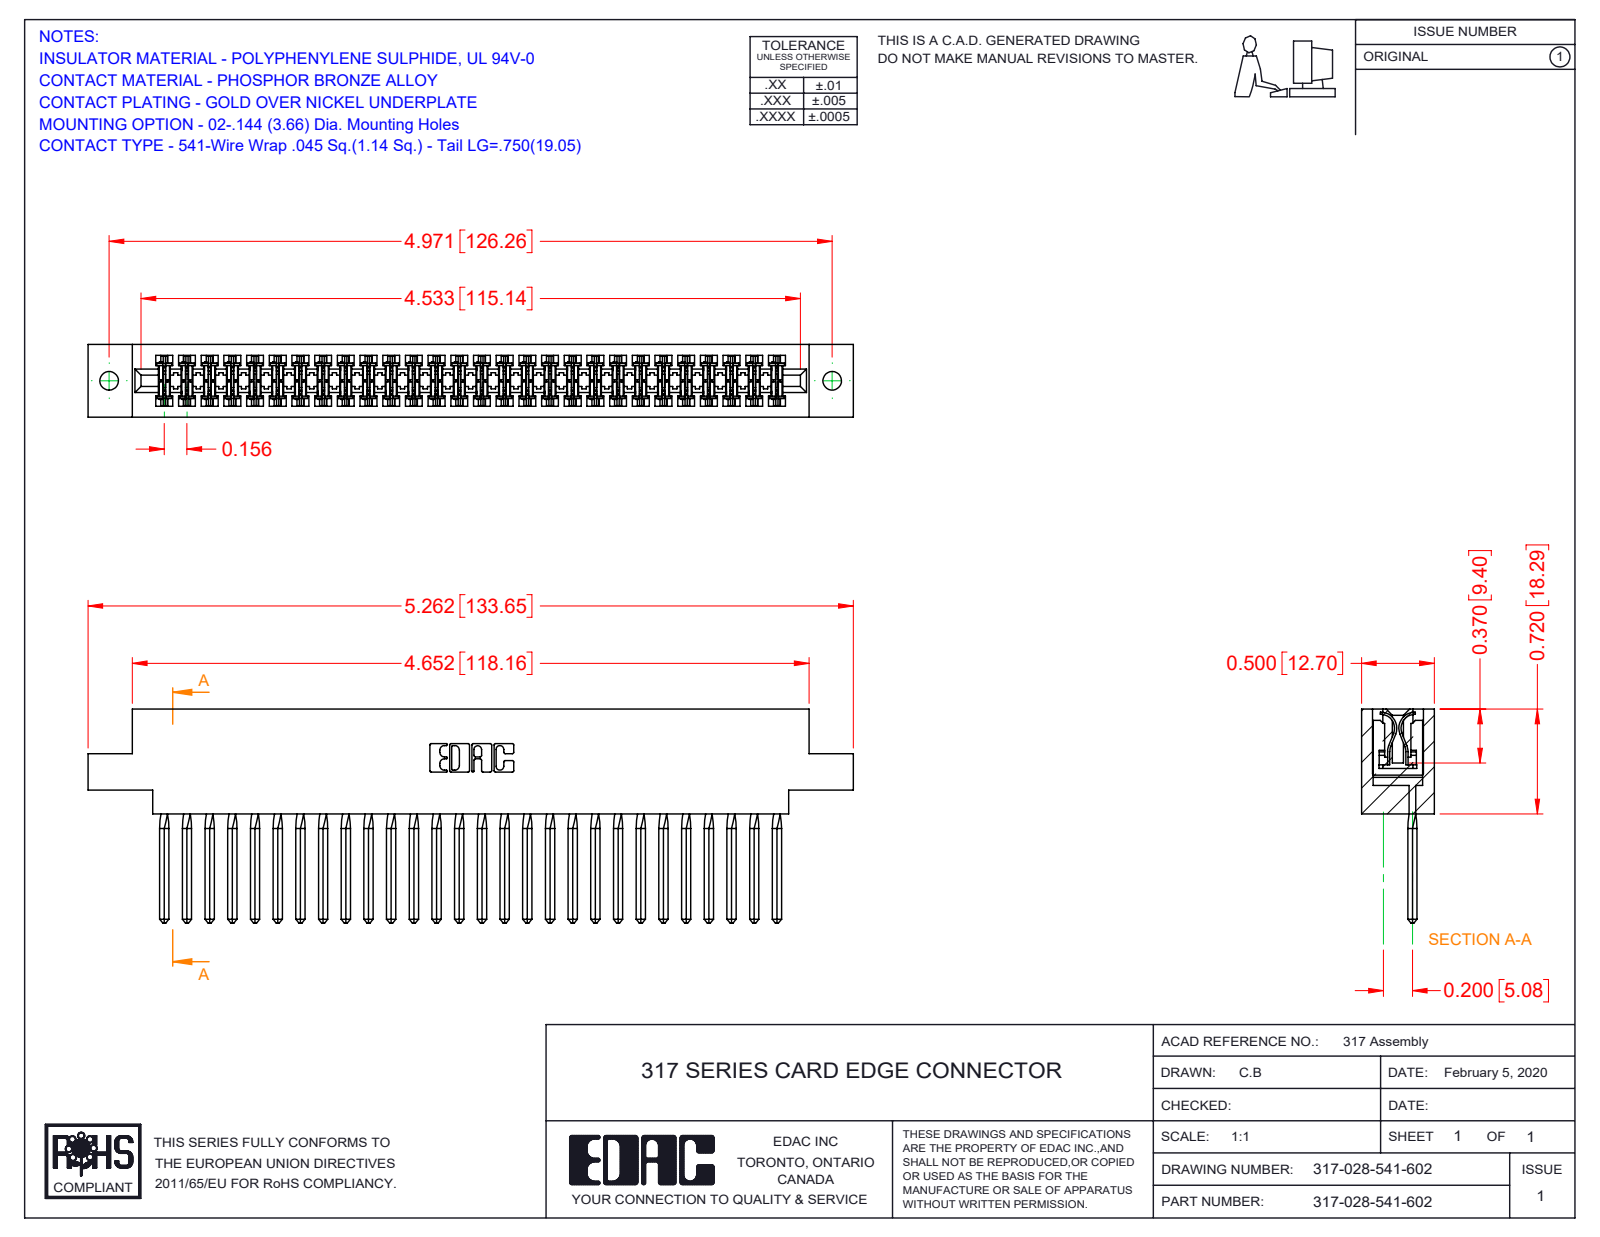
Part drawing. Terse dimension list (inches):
name: 317-028-541-602; 317-290-002_541; 317 Part_.144 Dia
written by: SolidWorks 2016 (CONFIG_CONTROL_DESIGN)
unit: in
bodies: 29 solids, 4358 faces (3530 planar, 716 cylindrical, 112 other)
size: 5.262 × 1.47 × 0.5
volume: 1.294 in³; area: 45.31 in²
holes: 2× ⌀0.128
rounds: 56× R0.015, 22× R0.01, 6× R0.007, 6× R0.031, 3× R0.026, 2× R0.095, 2× R0.1, 2× R0.11
face distances: 0.5, 0.075, 0.425, 0.35, 0.11, 0.195, 0.72, 0.115, 0.211, 0.289
hole spacings: 4.971
